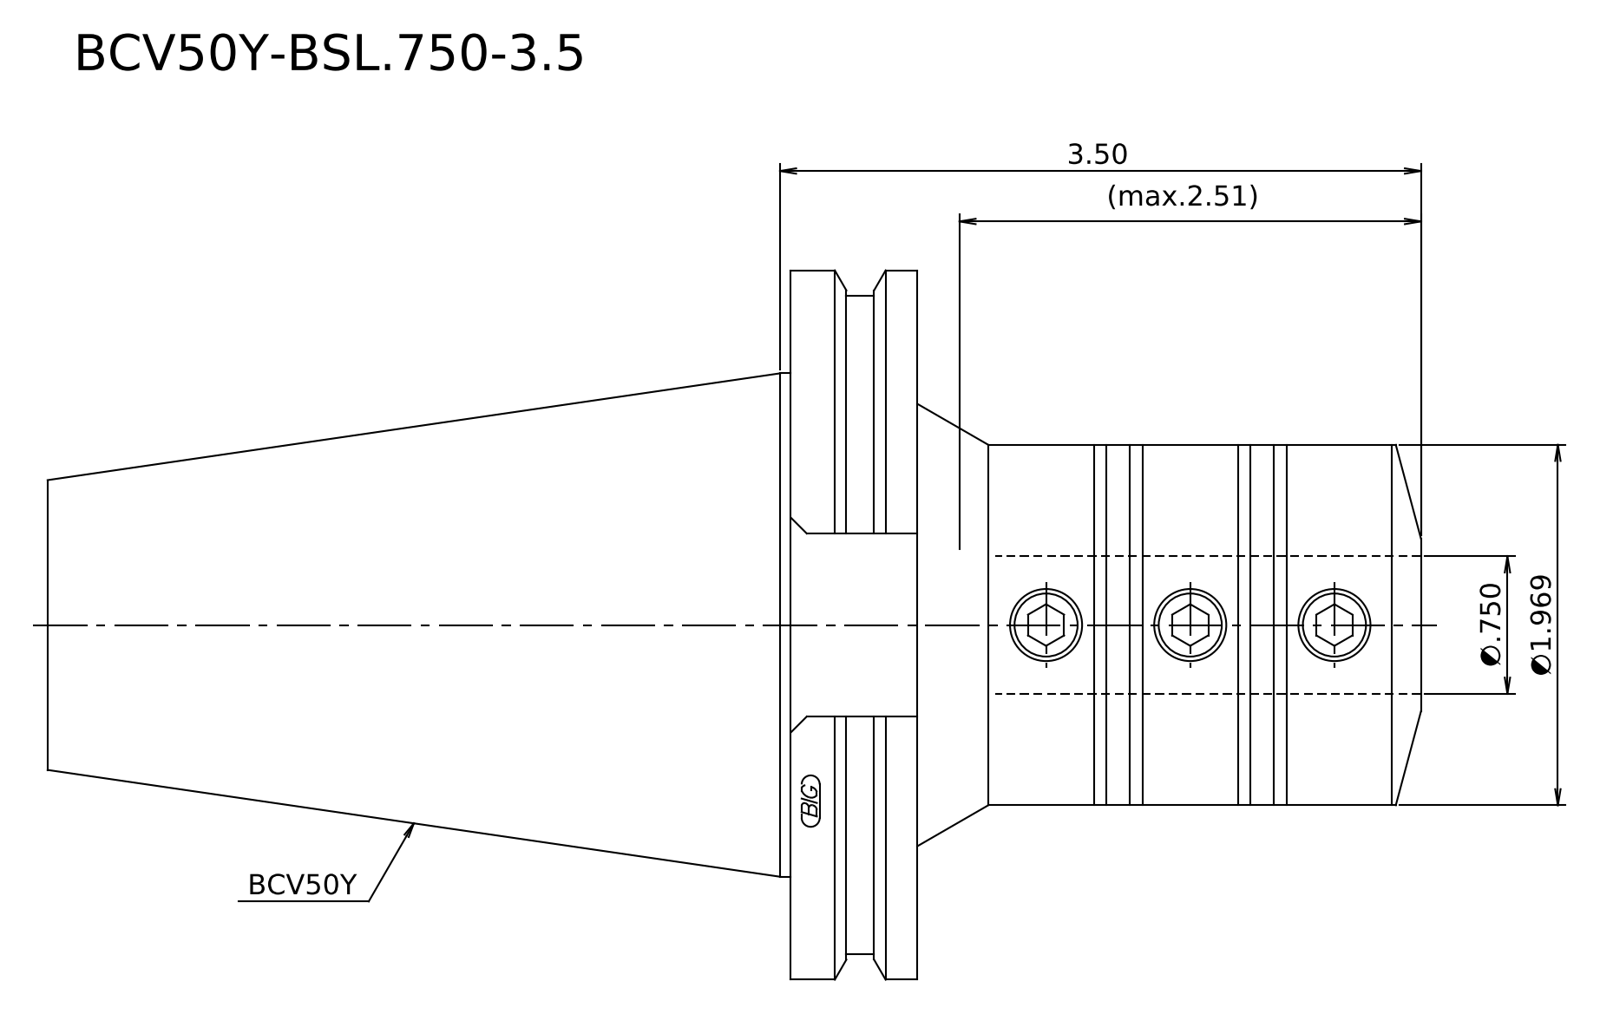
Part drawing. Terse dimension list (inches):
written by: Kubotek KeyCreator 2011 V10.0.2 (22737) (automotive_design)
unit: in
bodies: 1 solid, 16 faces (6 planar, 5 cylindrical, 5 other)
size: 7.5 × 3.875 × 3.875
volume: 31.75 in³; area: 73.46 in²
bosses: 1× ⌀3.875, 1× ⌀3.594, 1× ⌀2.75, 1× ⌀1.969
face distances: 0.691, 4.75, 4.059, 2.75, 3.441, 7.5, 2.987, 0.237, 0.454, 4.513
